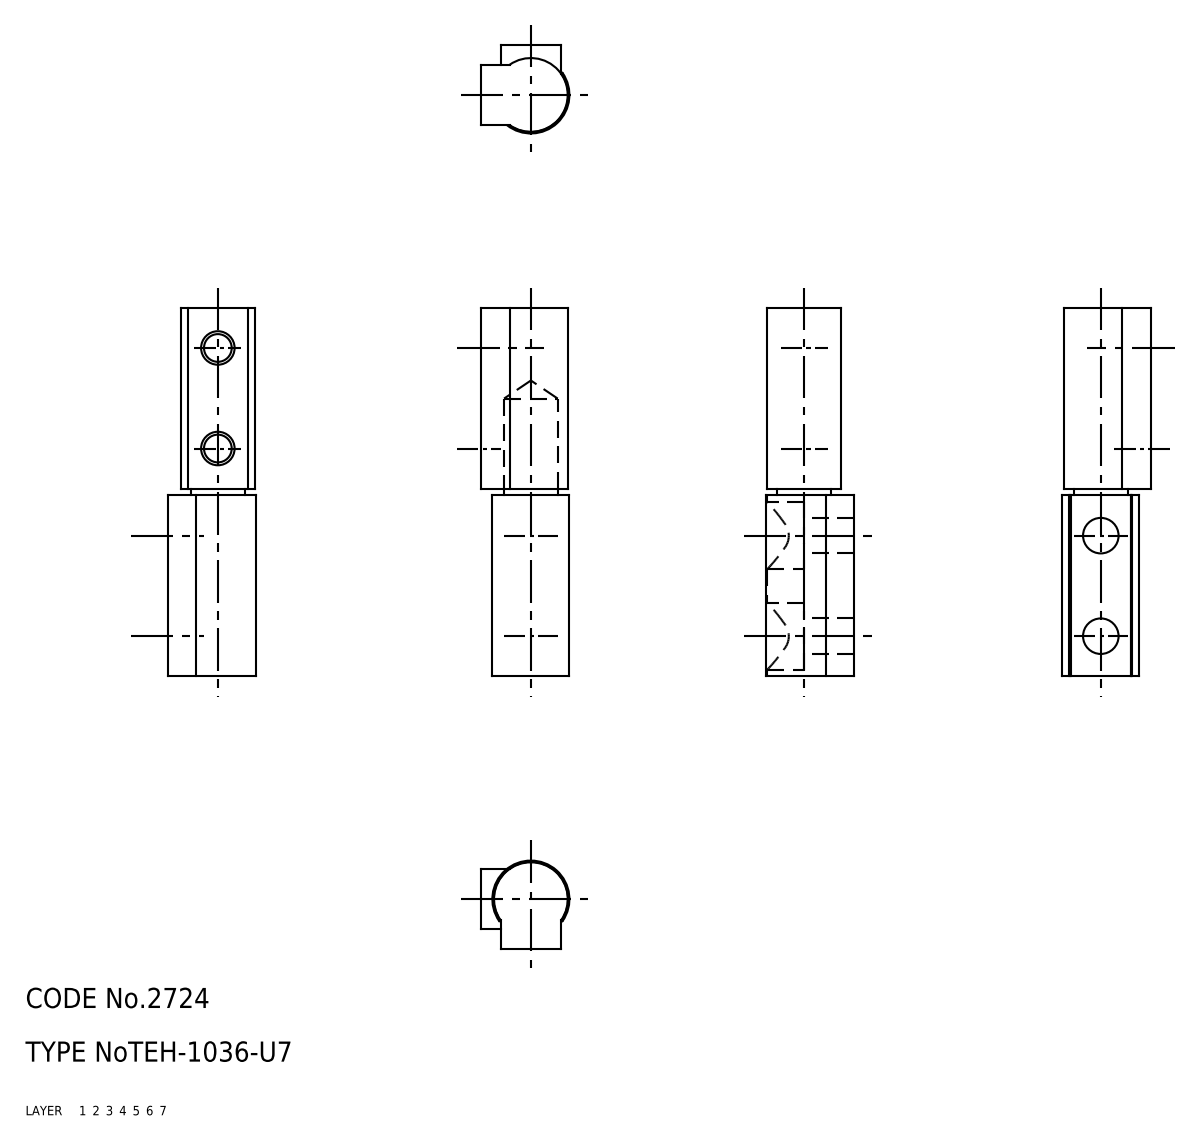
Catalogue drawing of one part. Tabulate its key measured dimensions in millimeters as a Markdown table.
| quantity | value |
| --- | --- |
| part name | hinge pieces_B; hinge pieces_A; cover; TEH_1036_U7_4258_36 |
| STEP written by | CADfix (AUTOMOTIVE_DESIGN) |
| units | millimeters |
| bodies | 3 solids, 43 faces (0 planar, 0 cylindrical, 43 other) |
| overall size | 55 × 13.25 × 13.25 |
| volume | 5 213 mm³ |
| surface area | 5 395 mm² |
